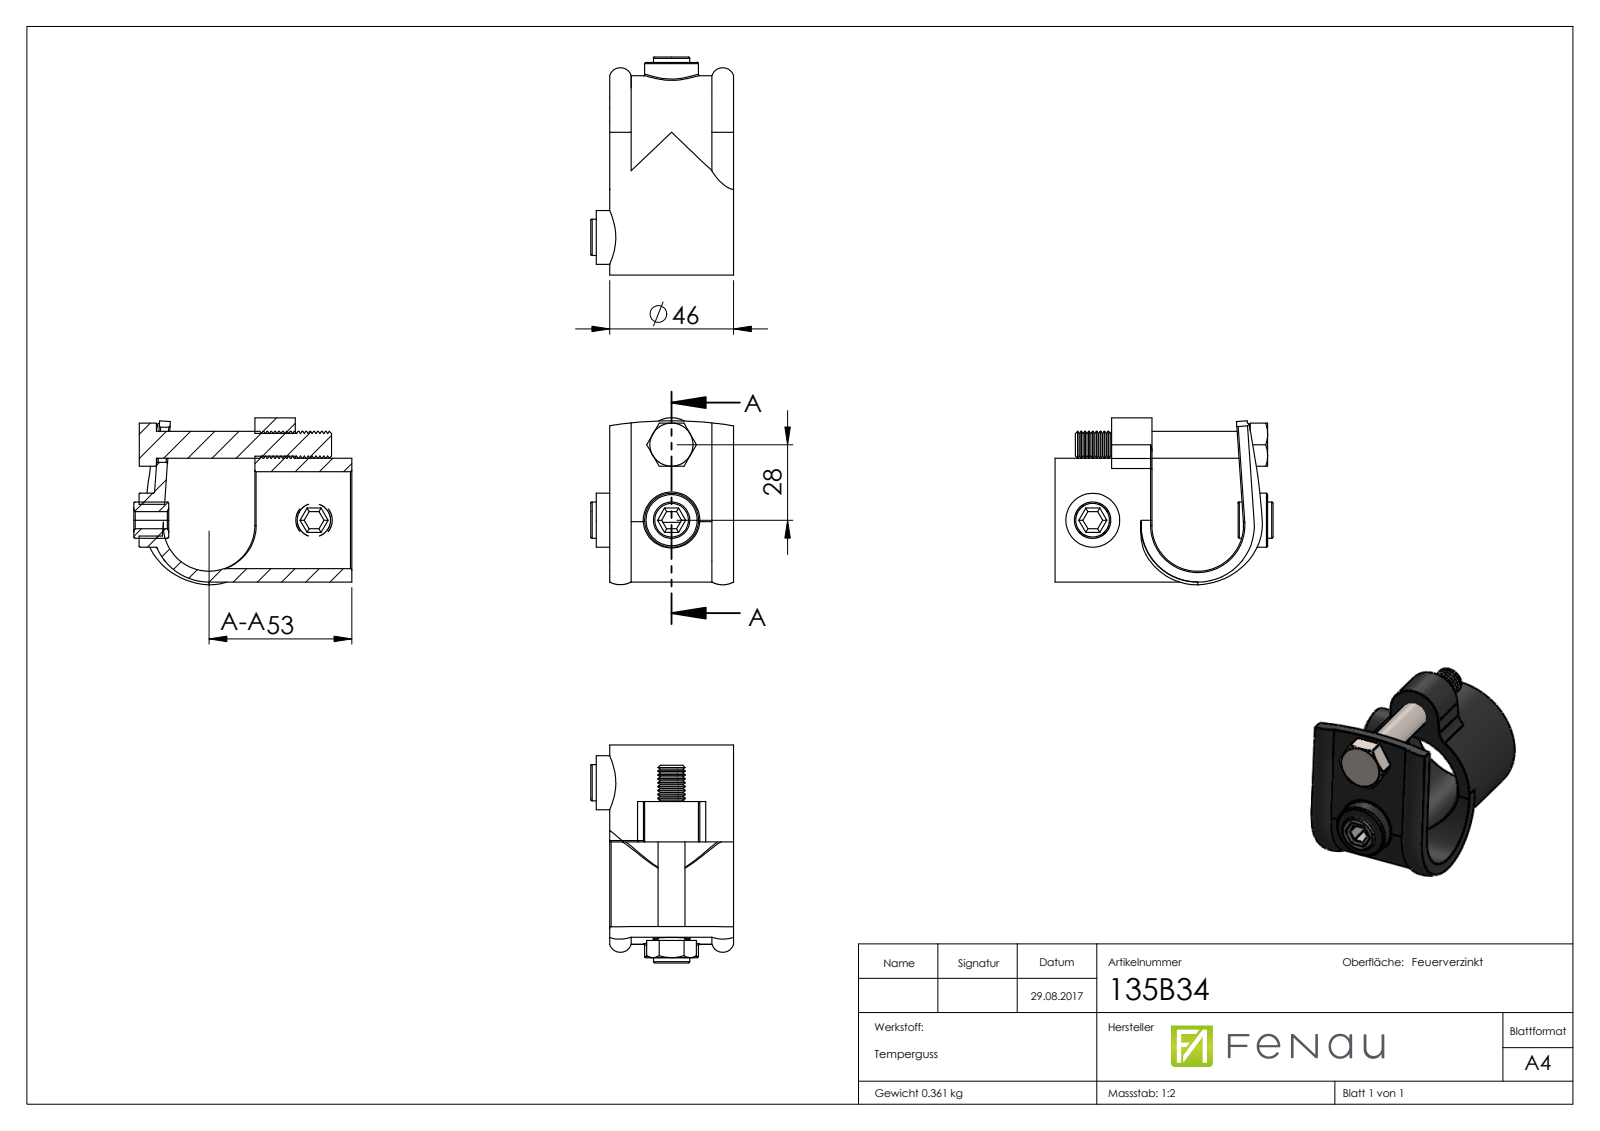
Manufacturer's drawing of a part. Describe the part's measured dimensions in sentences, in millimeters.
The part is named "135-C42 Teil1_135-B34 Teil1; 135-B34 Teil2; 135-B34; hex bolt gradeb_din (+2 more)". Its 3-D file was written by "SolidWorks 2018 (CONFIG_CONTROL_DESIGN)". It is 4 solids with 167 faces: 41 planar, 64 cylindrical and 62 other. Overall it measures 80.95 by 62 by 53 millimeters. Its volume is 54 609 cubic millimeters and its surface area 27 584 square millimeters. Round holes: 2 of diameter 11.8, 1 of diameter 8.5, 1 of diameter 13, 1 of diameter 36. Round bosses or shafts: 2 of diameter 20, 2 of diameter 13.5, 1 of diameter 46, 1 of diameter 10. Partial cylindrical surfaces (rounded edges, fillets, slot ends): 24 of radius 2, 3 of radius 0.5, 2 of radius 5, 2 of radius 21, 1 of radius 10, 1 of radius 17, 1 of radius 140.16. The main face-to-face distances are 4, 36, 46, 6.4, 15, 21, 5, 51, 78.91, 57.91. The hole center spacings are 28.
